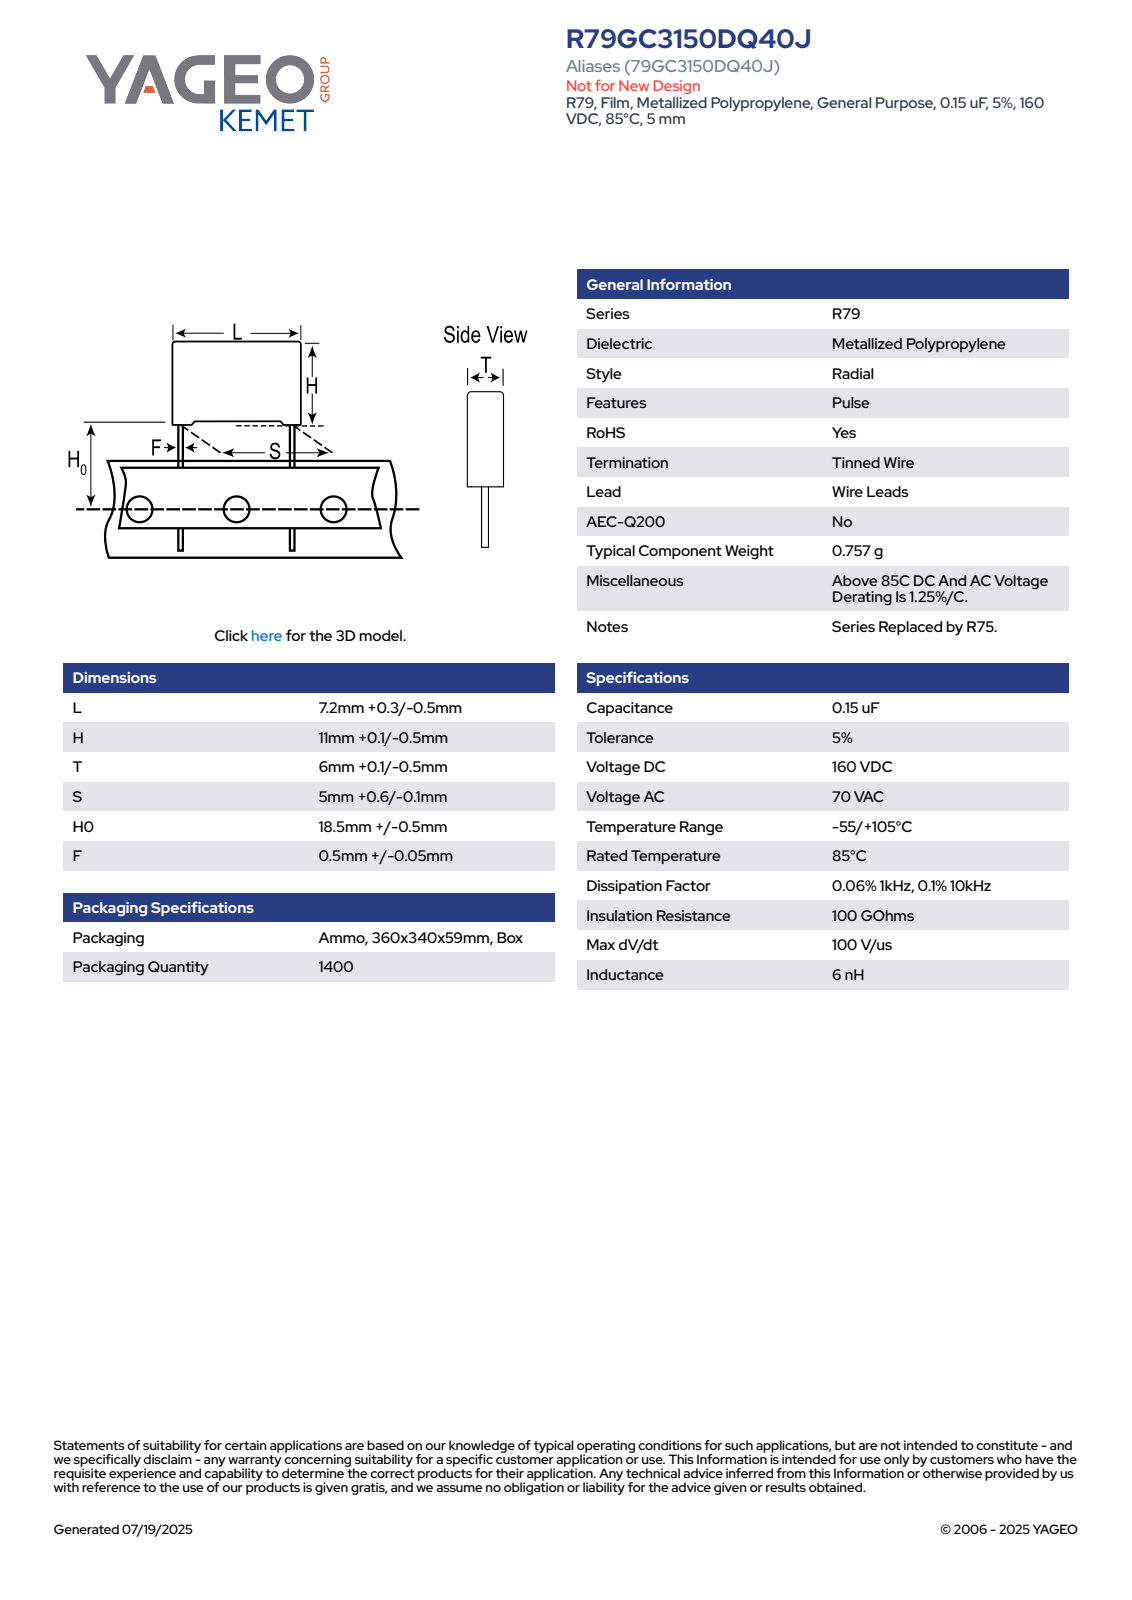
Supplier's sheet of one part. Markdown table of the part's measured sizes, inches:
| quantity | value |
| --- | --- |
| part name | CFR_RB2_7.2X11X6_L7.5H11.1T6.1S5H019F0.55 |
| STEP written by | SolidWorks 2020 (AUTOMOTIVE_DESIGN) |
| units | inches |
| bodies | 4 solids, 85 faces (77 planar, 8 cylindrical, 0 other) |
| overall size | 1.185 × 0.295 × 0.241 |
| volume | 0.03 in³ |
| surface area | 0.738 in² |
| round bosses / shafts (diameter × count) | 0.022 × 2 |
| partial cylindrical surfaces (radius × count) | 0.02 × 4 |
| main face-to-face distances | 0.24, 0.295, 0.407, 0.23, 0.285, 0.03, 0.437, 0.22, 0.276, 0.015 |
